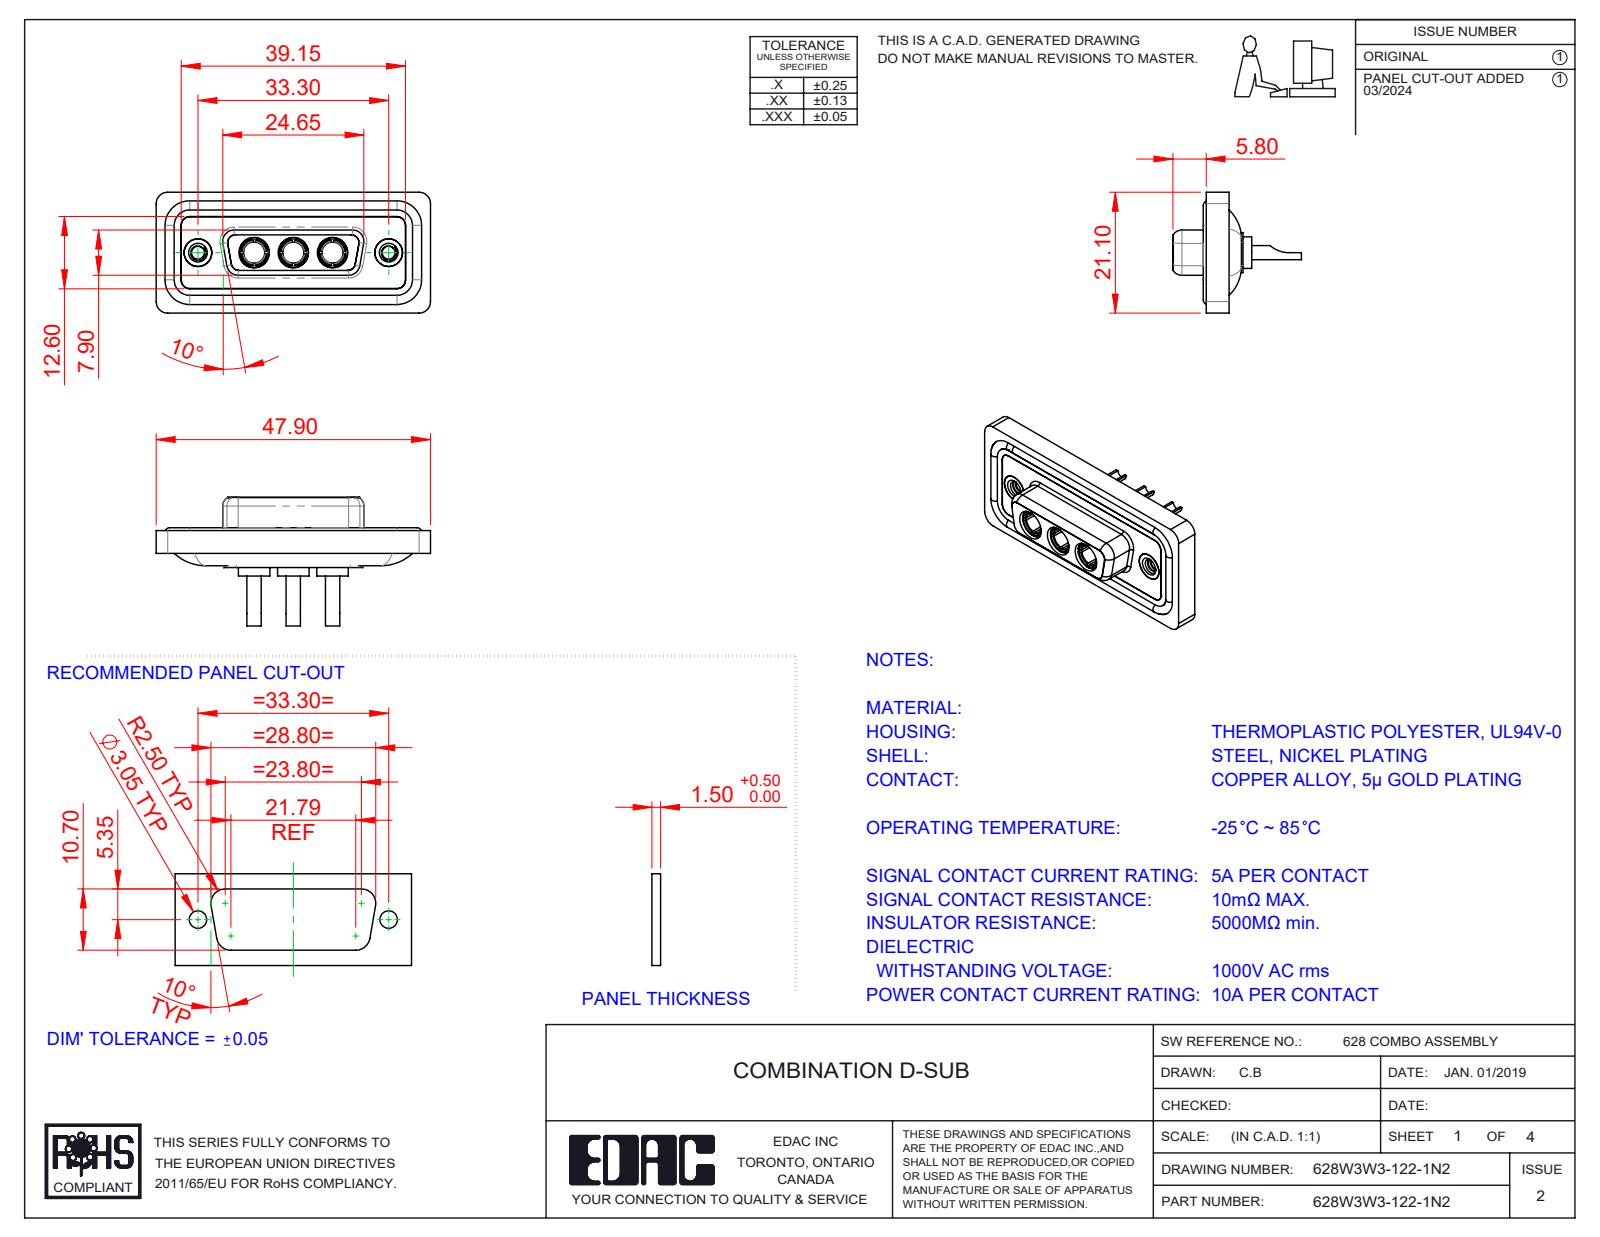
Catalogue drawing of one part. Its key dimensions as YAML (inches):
part_name: "628Combo Threaded Rivet_2; 628Combo Waterproof Housing_15 Contacts; Power Socket_10A SC; 628Combo Shell Front_15 Contacts (+3 more)"
step_written_by: "SolidWorks 2023 (CONFIG_CONTROL_DESIGN)"
units: inches
bodies: {solids: 13, faces: 623, planar: 198, cylindrical: 266, other: 159}
overall_size: [1.886, 0.884, 0.831]
volume: 0.367
surface_area: 15.32
round_holes:
  - {diameter: 0.191, count: 5}
  - {diameter: 0.067, count: 3}
  - {diameter: 0.146, count: 3}
  - {diameter: 0.209, count: 3}
  - {diameter: 0.089, count: 2}
  - {diameter: 0.157, count: 2}
  - {diameter: 0.159, count: 2}
  - {diameter: 0.197, count: 2}
round_bosses_or_shafts:
  - {diameter: 0.063, count: 4}
  - {diameter: 0.217, count: 3}
  - {diameter: 0.205, count: 3}
  - {diameter: 0.195, count: 3}
  - {diameter: 0.187, count: 3}
  - {diameter: 0.148, count: 3}
  - {diameter: 0.098, count: 3}
  - {diameter: 0.195, count: 2}
partial_cylinders:
  - {radius: 0.059, count: 22}
  - {radius: 0.079, count: 20}
  - {radius: 0.053, count: 12}
  - {radius: 0.063, count: 8}
  - {radius: 0.01, count: 4}
  - {radius: 0.02, count: 4}
  - {radius: 0.024, count: 4}
  - {radius: 0.026, count: 4}
face_to_face_distances: [0.016, 0.071, 0.063, 0.02, 0.293, 0.043, 0.114, 0.222, 0.278, 0.26]
hole_center_spacings: [0.27, 0.386, 0.656, 0.925, 0.539, 1.311]
